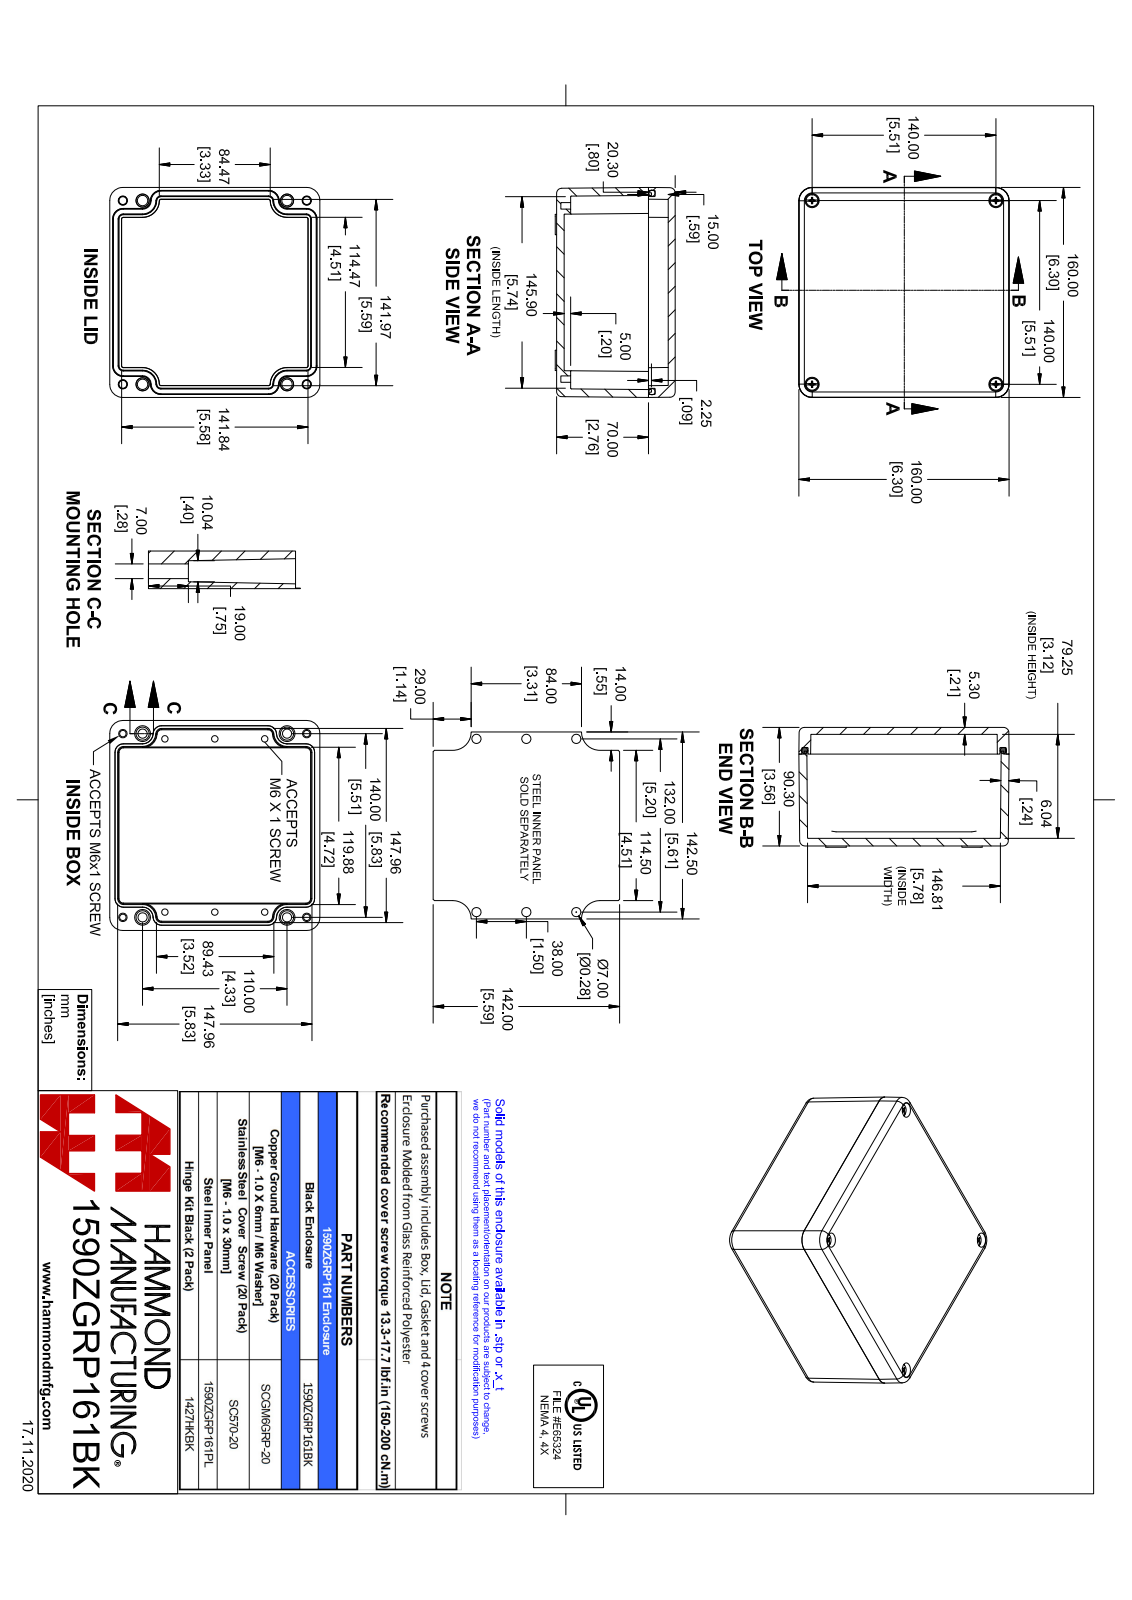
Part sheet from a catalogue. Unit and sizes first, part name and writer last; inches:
Units: inches
Overall size (bounding box): 6.299 × 6.299 × 3.594
Round holes (diameter × count): ⌀0.194 ×10, ⌀0.236 ×4, ⌀0.252 ×4, ⌀0.276 ×4, ⌀0.425 ×4
Round bosses / shafts (diameter × count): ⌀0.189 ×6, ⌀0.231 ×4, ⌀0.208 ×4
Partial cylindrical surfaces — rounded edges, fillets, slot ends (radius × count): R0.02 ×18, R0.059 ×8, R0.157 ×8, R0.394 ×8
Main face-to-face distances: 3.555, 3.346, 0.209, 0.226, 3.12, 3.329, 0.228, 0.238, 6.299, 2.53
Hole centre spacings: 5.512, 0.591, 0.687, 1.27, 1.496, 2.171, 2.76, 3.665
Volume: 42.25 in³ · Surface area: 358.8 in²
Bodies: 7 solids, 459 faces (211 planar, 88 cylindrical, 160 other)
Part name (STEP PRODUCT): 1590ZGRP161BK
STEP written by: SolidWorks 2021 (AUTOMOTIVE_DESIGN)
